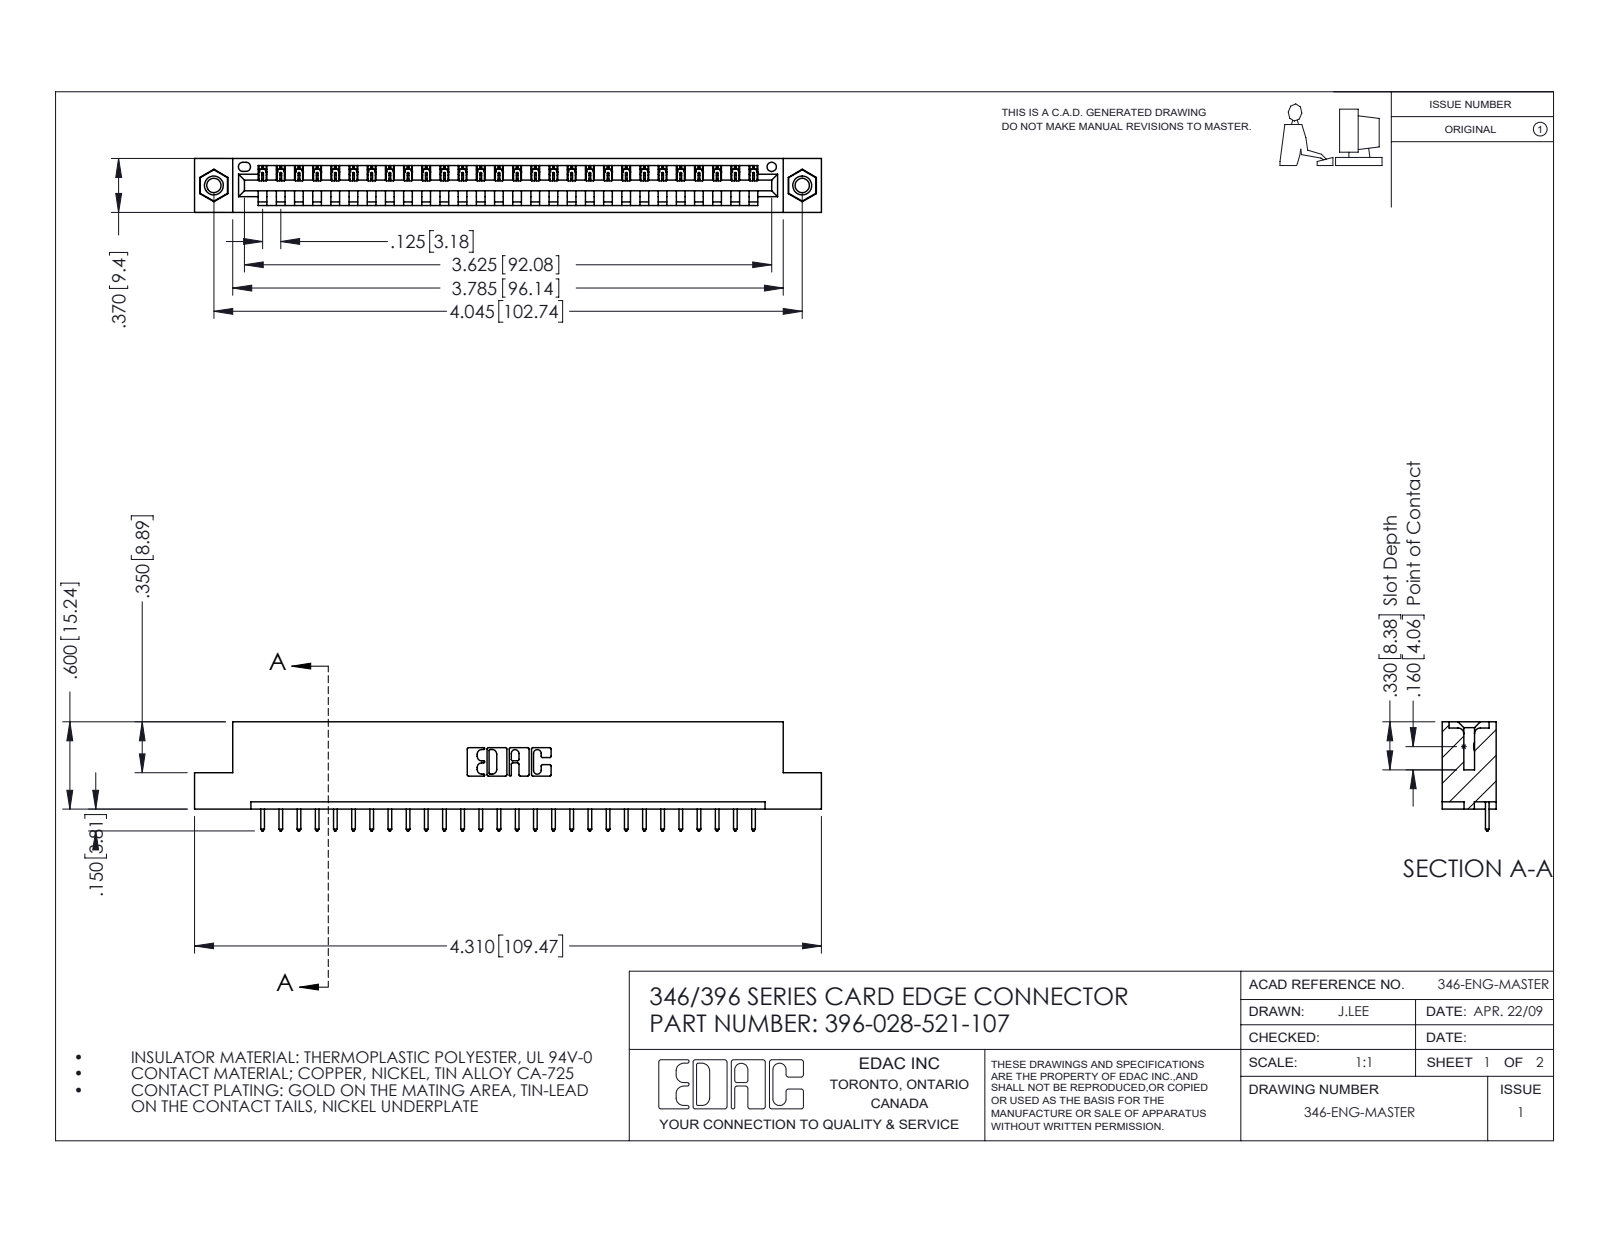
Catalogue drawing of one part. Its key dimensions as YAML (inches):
part_name: "396-028-521-107; 346 Part_Flush Mounting Lugs - 0.156 Dia-TI; 345-250-001_345-250-005-103; 345-292-001_345-293-121"
step_written_by: "SolidWorks 2016 (CONFIG_CONTROL_DESIGN)"
units: inches
bodies: {solids: 31, faces: 1806, planar: 1228, cylindrical: 562, other: 16}
overall_size: [4.31, 0.75, 0.37]
volume: 0.628
surface_area: 19.26
round_holes:
  - {diameter: 0.098, count: 2}
  - {diameter: 0.125, count: 2}
  - {diameter: 0.156, count: 2}
  - {diameter: 0.064, count: 1}
round_bosses_or_shafts:
  - {diameter: 0.155, count: 2}
partial_cylinders:
  - {radius: 0.006, count: 56}
  - {radius: 0.01, count: 56}
  - {radius: 0.01, count: 22}
  - {radius: 0.007, count: 6}
  - {radius: 0.031, count: 6}
  - {radius: 0.026, count: 3}
  - {radius: 0.031, count: 2}
  - {radius: 0.04, count: 2}
face_to_face_distances: [0.048, 0.322, 0.37, 0.25, 0.072, 0.298, 0.025, 0.148, 0.222, 0.1]
hole_center_spacings: [0.246, 3.837, 4.045]
